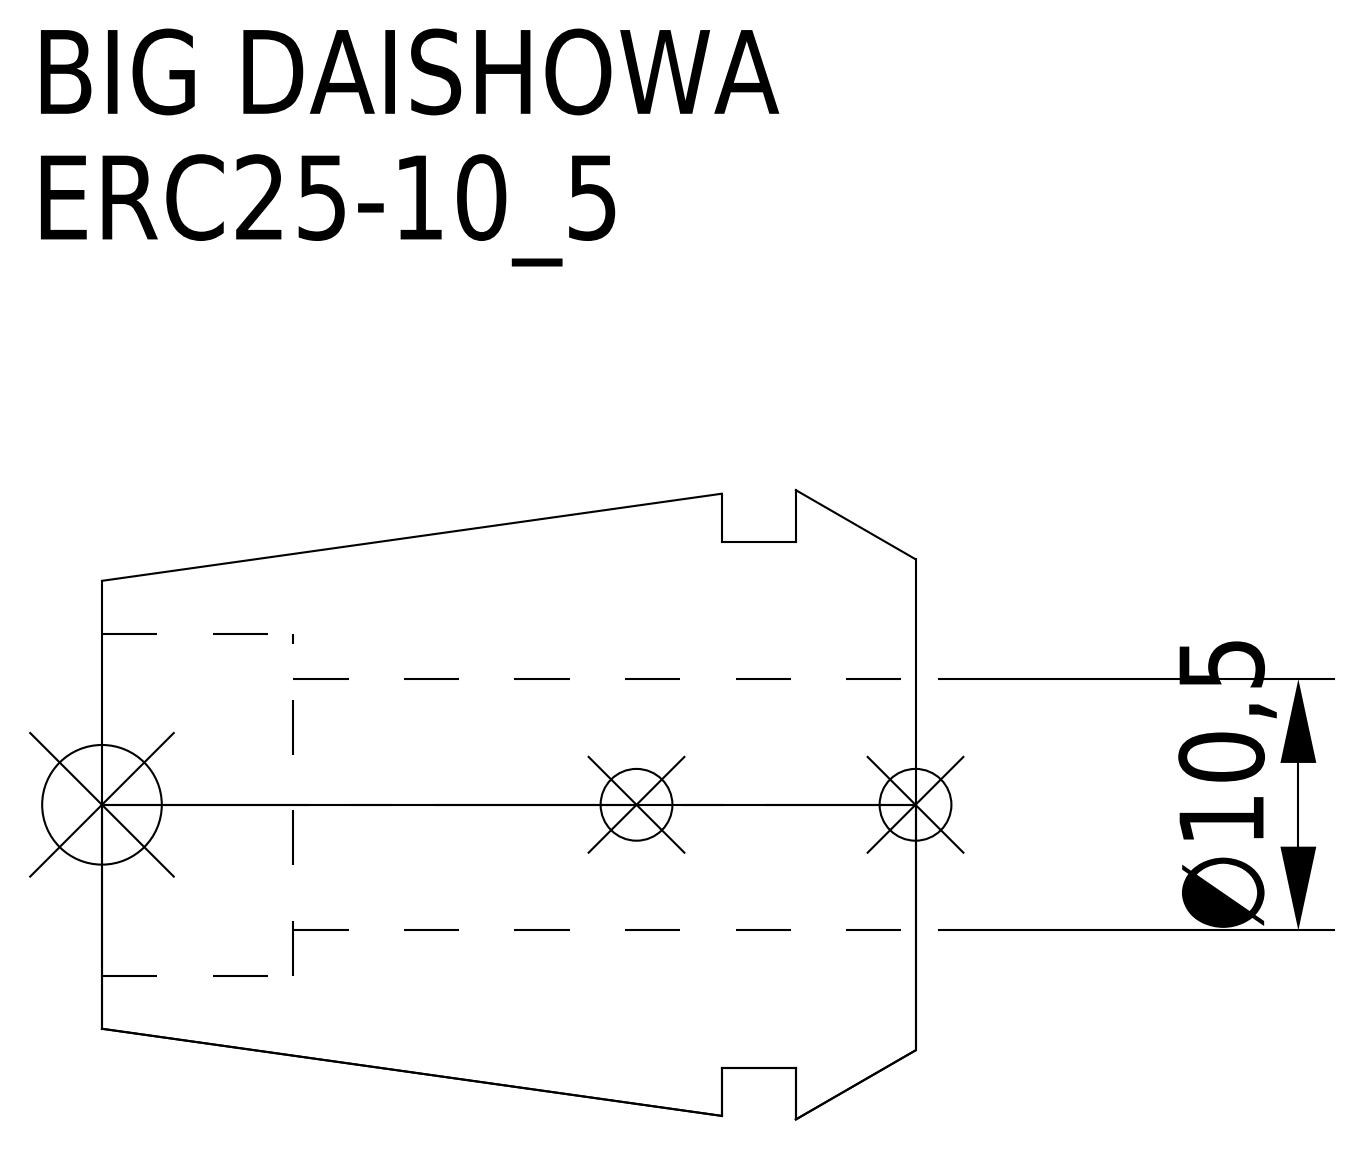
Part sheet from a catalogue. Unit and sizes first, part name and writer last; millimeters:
Units: millimetres
Overall size (bounding box): 34 × 26.3 × 26.3
Round holes (diameter × count): ⌀10.5 ×1, ⌀14.3 ×1
Round bosses / shafts (diameter × count): ⌀22 ×1
Main face-to-face distances: 5, 8.1, 3.1, 34, 29, 25.9, 26, 21, 17.9, 8
Volume: 10 067 mm³ · Surface area: 4 440 mm²
Bodies: 1 solid, 15 faces (5 planar, 6 cylindrical, 4 other)
Part name (STEP PRODUCT): ERC25-10_5
STEP written by: CREO PARAMETRIC BY PTC INC, 2016380 (AUTOMOTIVE_DESIGN)
